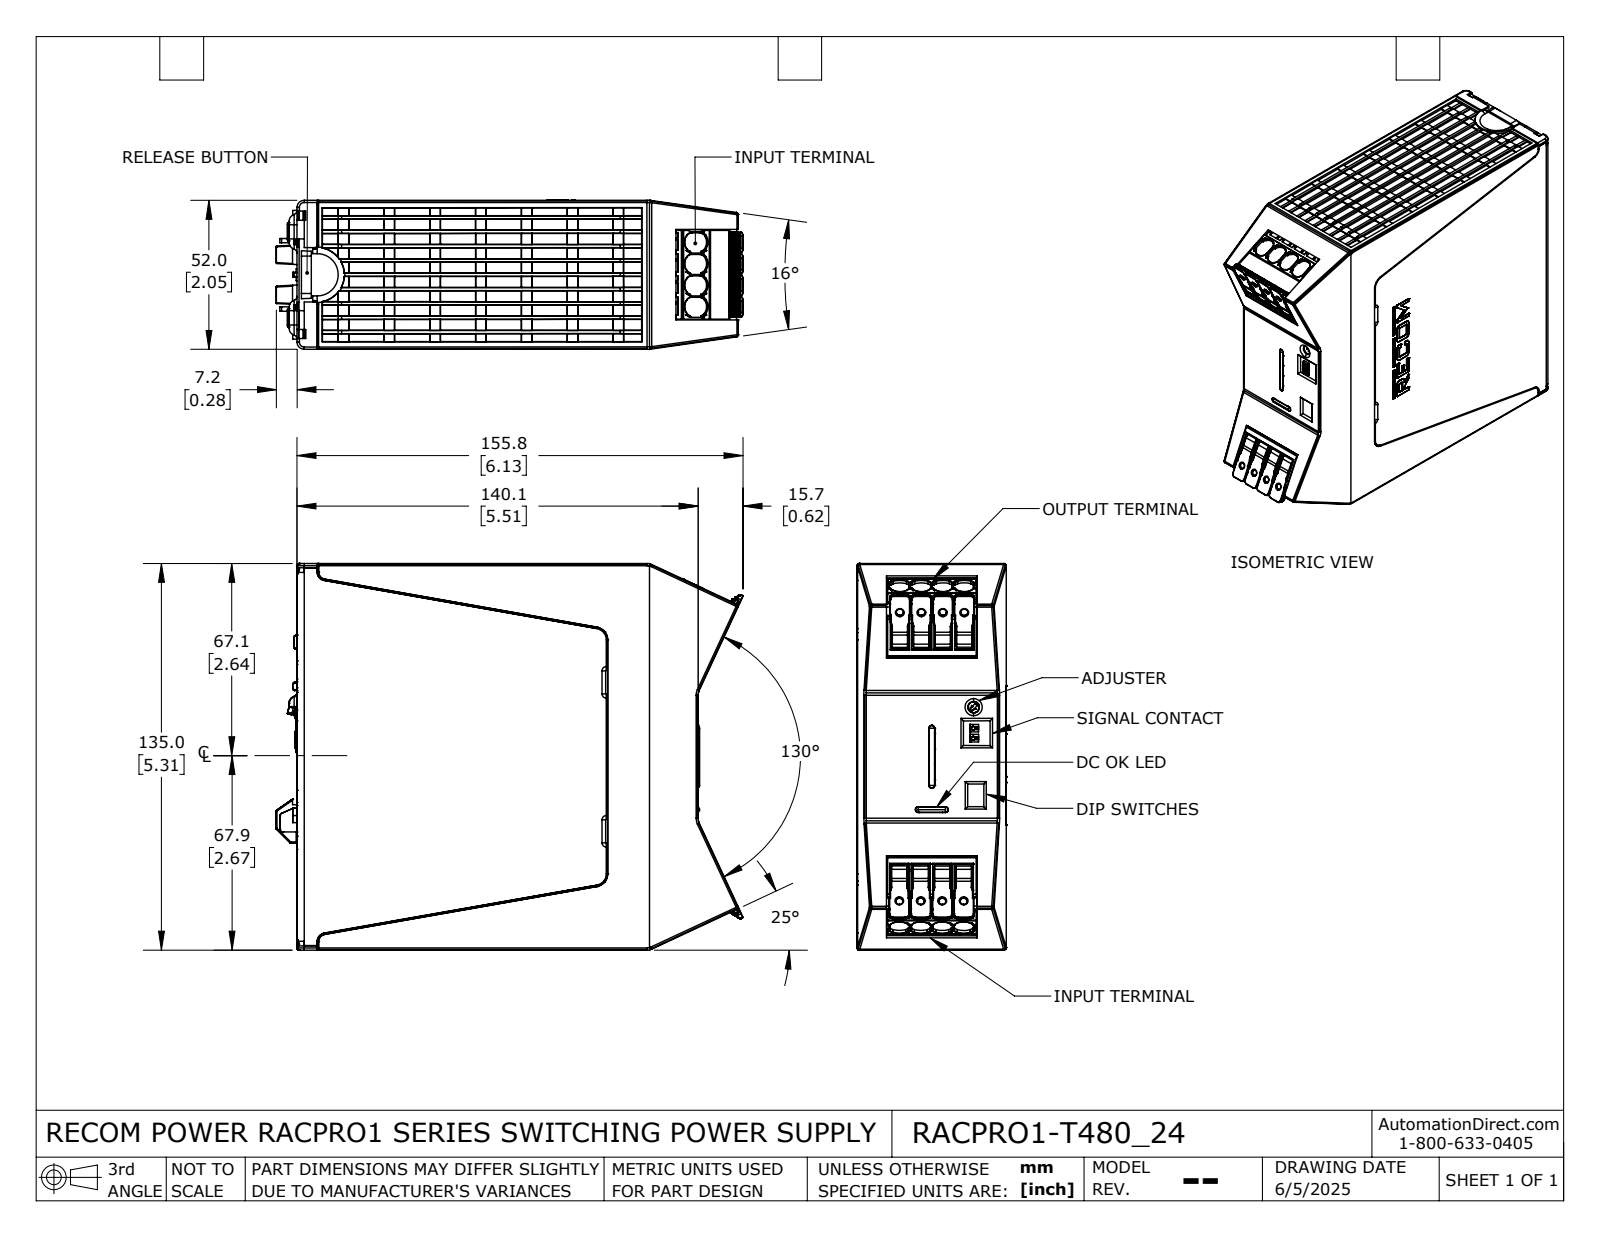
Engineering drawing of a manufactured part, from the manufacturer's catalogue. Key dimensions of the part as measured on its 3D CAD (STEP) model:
Part name (STEP PRODUCT): RACPRO1-T480_24
STEP written by: SolidWorks 2024 (AUTOMOTIVE_DESIGN)
Units: inches
Bodies: 1 solid, 3461 faces (1621 planar, 1042 cylindrical, 798 other)
Overall size (bounding box): 6.419 × 5.315 × 2.049
Volume: 60.25 in³ · Surface area: 152 in²
Round holes (diameter × count): ⌀0.098 ×8, ⌀0.079 ×2, ⌀0.157 ×1, ⌀0.209 ×1
Round bosses / shafts (diameter × count): ⌀0.197 ×2, ⌀0.15 ×1
Partial cylindrical surfaces — rounded edges, fillets, slot ends (radius × count): R0.008 ×248, R0.039 ×60, R0.098 ×39, R0.012 ×38, R0.02 ×31, R0.118 ×25, R0.031 ×24, R0.059 ×22
Main face-to-face distances: 2.047, 0.059, 1.988, 5.265, 0.196, 0.018, 0.392, 0.02, 5.515, 5.297
Hole centre spacings: 0.295, 0.591, 0.886, 1.504, 1.575, 2.018
